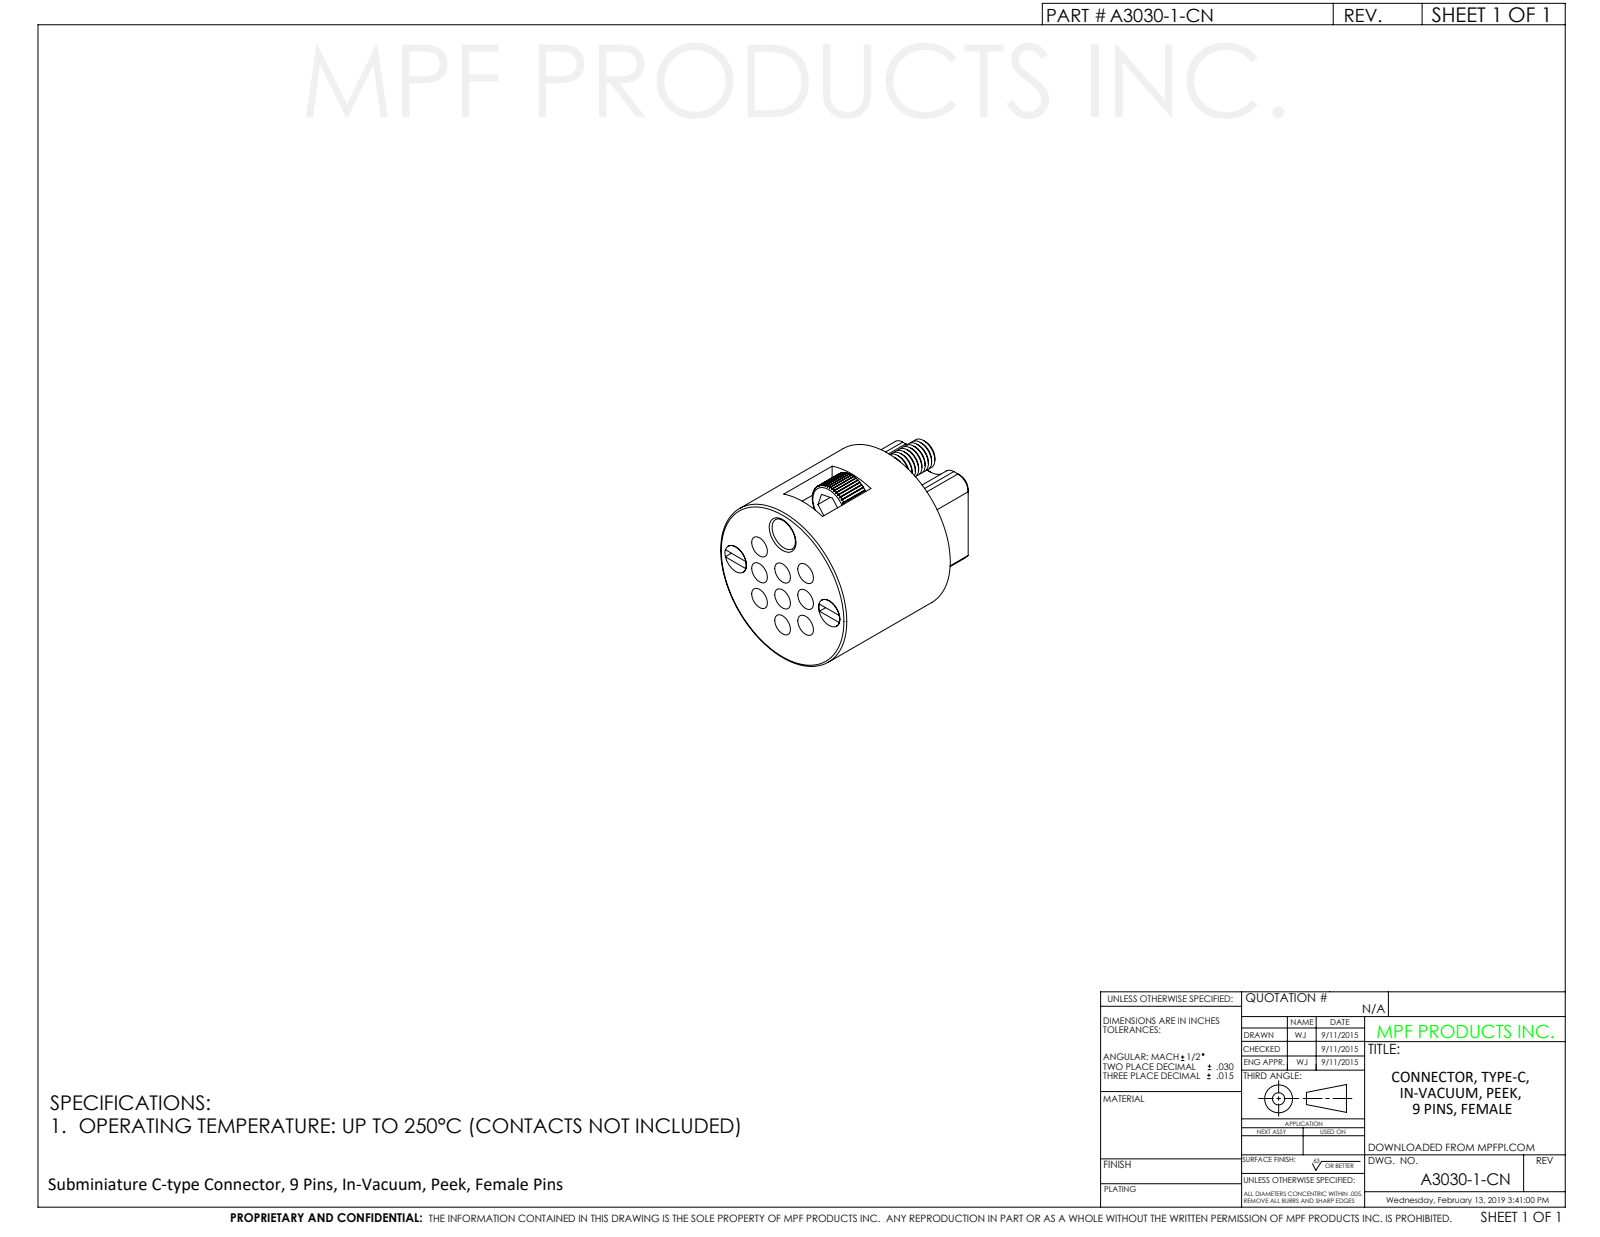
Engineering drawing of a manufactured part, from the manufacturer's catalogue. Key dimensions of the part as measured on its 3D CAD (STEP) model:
Part name (STEP PRODUCT): A3030-1-CN
STEP written by: SolidWorks 2012 (CONFIG_CONTROL_DESIGN)
Units: millimetres
Bodies: 1 solid, 404 faces (196 planar, 132 cylindrical, 76 other)
Overall size (bounding box): 18.52 × 15.49 × 15.49
Volume: 2 412 mm³ · Surface area: 2 421 mm²
Round holes (diameter × count): ⌀1.17 ×9, ⌀1.93 ×9, ⌀0.81 ×1, ⌀2.95 ×1
Round bosses / shafts (diameter × count): ⌀2.62 ×2, ⌀15.49 ×1, ⌀4.32 ×1, ⌀2.79 ×1
Partial cylindrical surfaces — rounded edges, fillets, slot ends (radius × count): R1.27 ×5, R1.32 ×1, R2.4 ×1, R2.41 ×1, R5.84 ×1
Main face-to-face distances: 12.95, 4.44, 8.51, 5.46, 5.54, 9.98, 18.49, 11, 1.02, 7.49
Hole centre spacings: 3.15, 2.77, 5.02, 3.17, 5.68, 6.32, 3.91, 5.54
